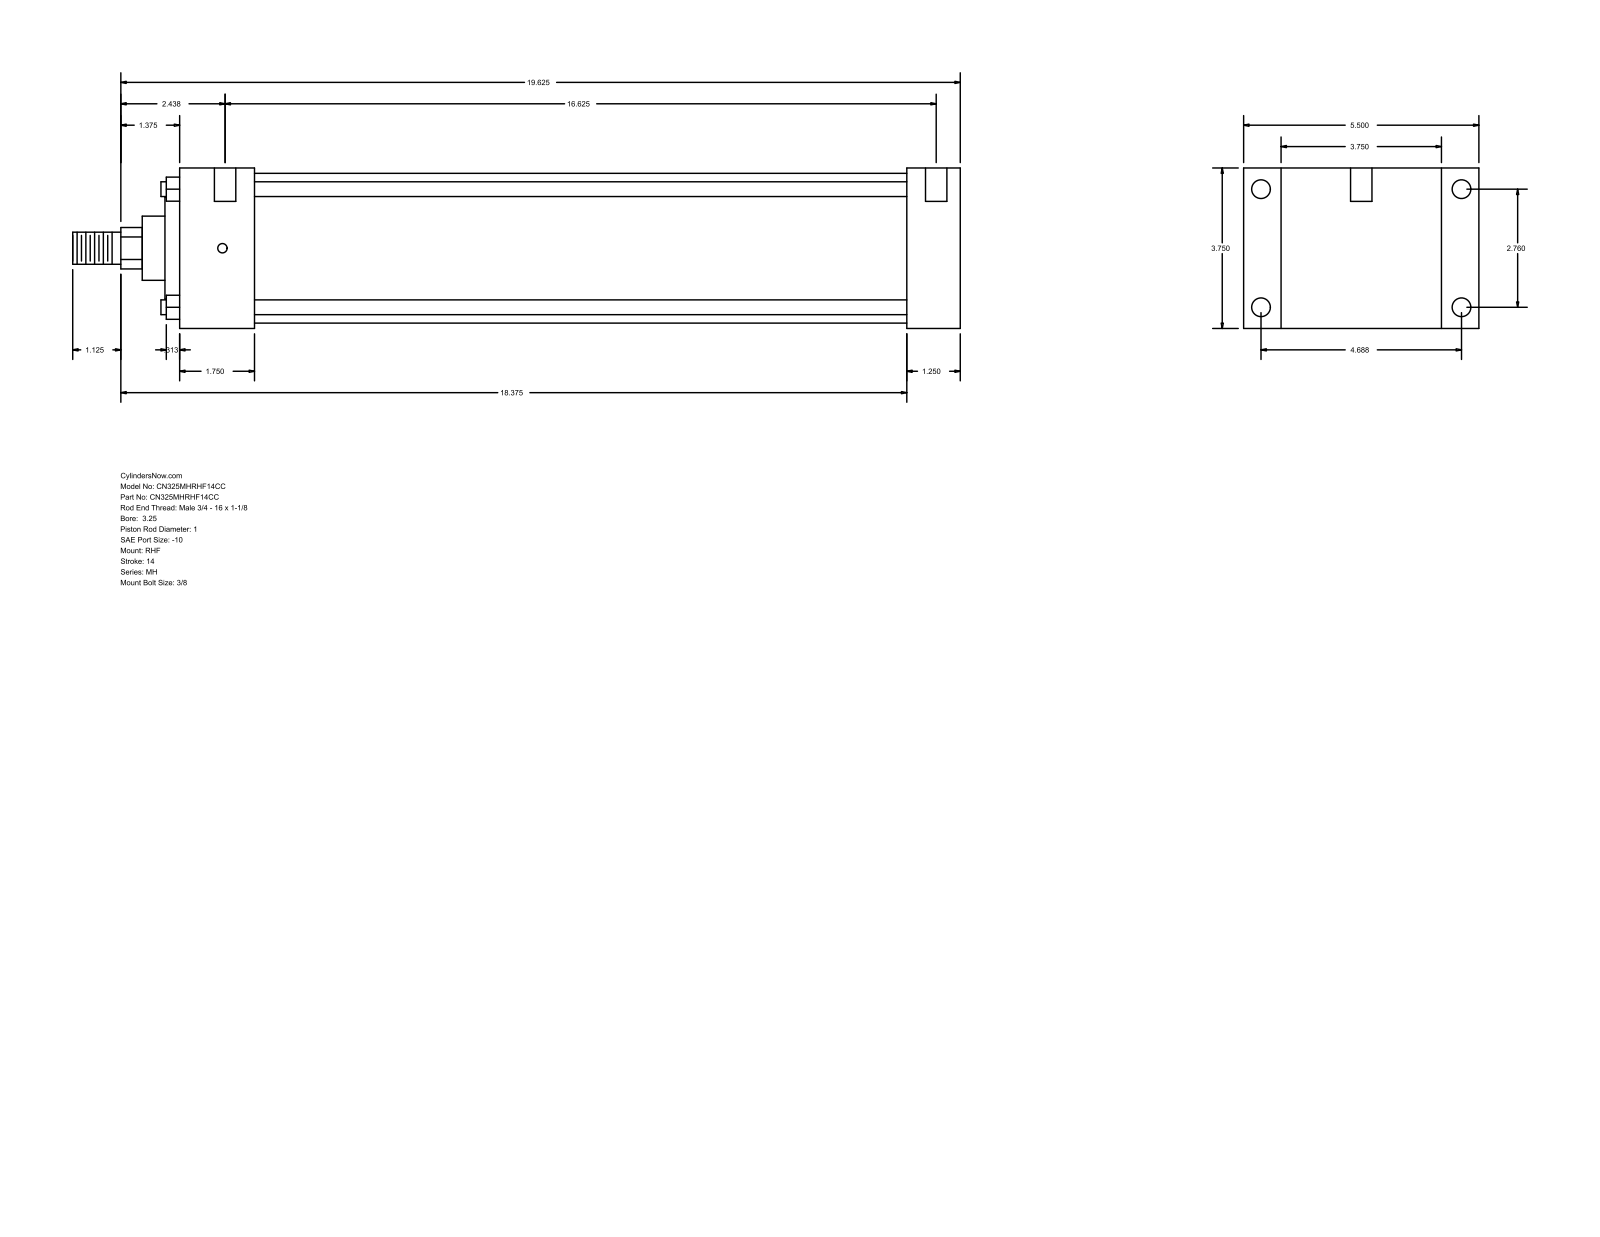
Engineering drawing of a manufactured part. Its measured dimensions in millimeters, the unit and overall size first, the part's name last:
Units: millimetres
Overall size (bounding box): 527.05 × 139.7 × 95.25
Round holes (diameter × count): ⌀5.56 ×4, ⌀11.13 ×4, ⌀12.7 ×2
Round bosses / shafts (diameter × count): ⌀8.76 ×4, ⌀88.9 ×1, ⌀60.33 ×1, ⌀38.1 ×1, ⌀25.4 ×1, ⌀19.05 ×1
Partial cylindrical surfaces — rounded edges, fillets, slot ends (radius × count): R12.29 ×1
Main face-to-face distances: 95.24, 31.75, 22.23, 117.47, 431.81, 463.56, 139.7, 44.46, 387.35, 419.1
Hole centre spacings: 70.1, 119.06, 138.16, 428.62, 1.58, 4.76, 422.28, 423.86
Bodies: 0 solids, 90 faces (61 planar, 29 cylindrical, 0 other)
Part name (STEP PRODUCT): MH_RHF__0325_1
STEP written by: GSSL Pune (CONFIG_CONTROL_DESIGN)
